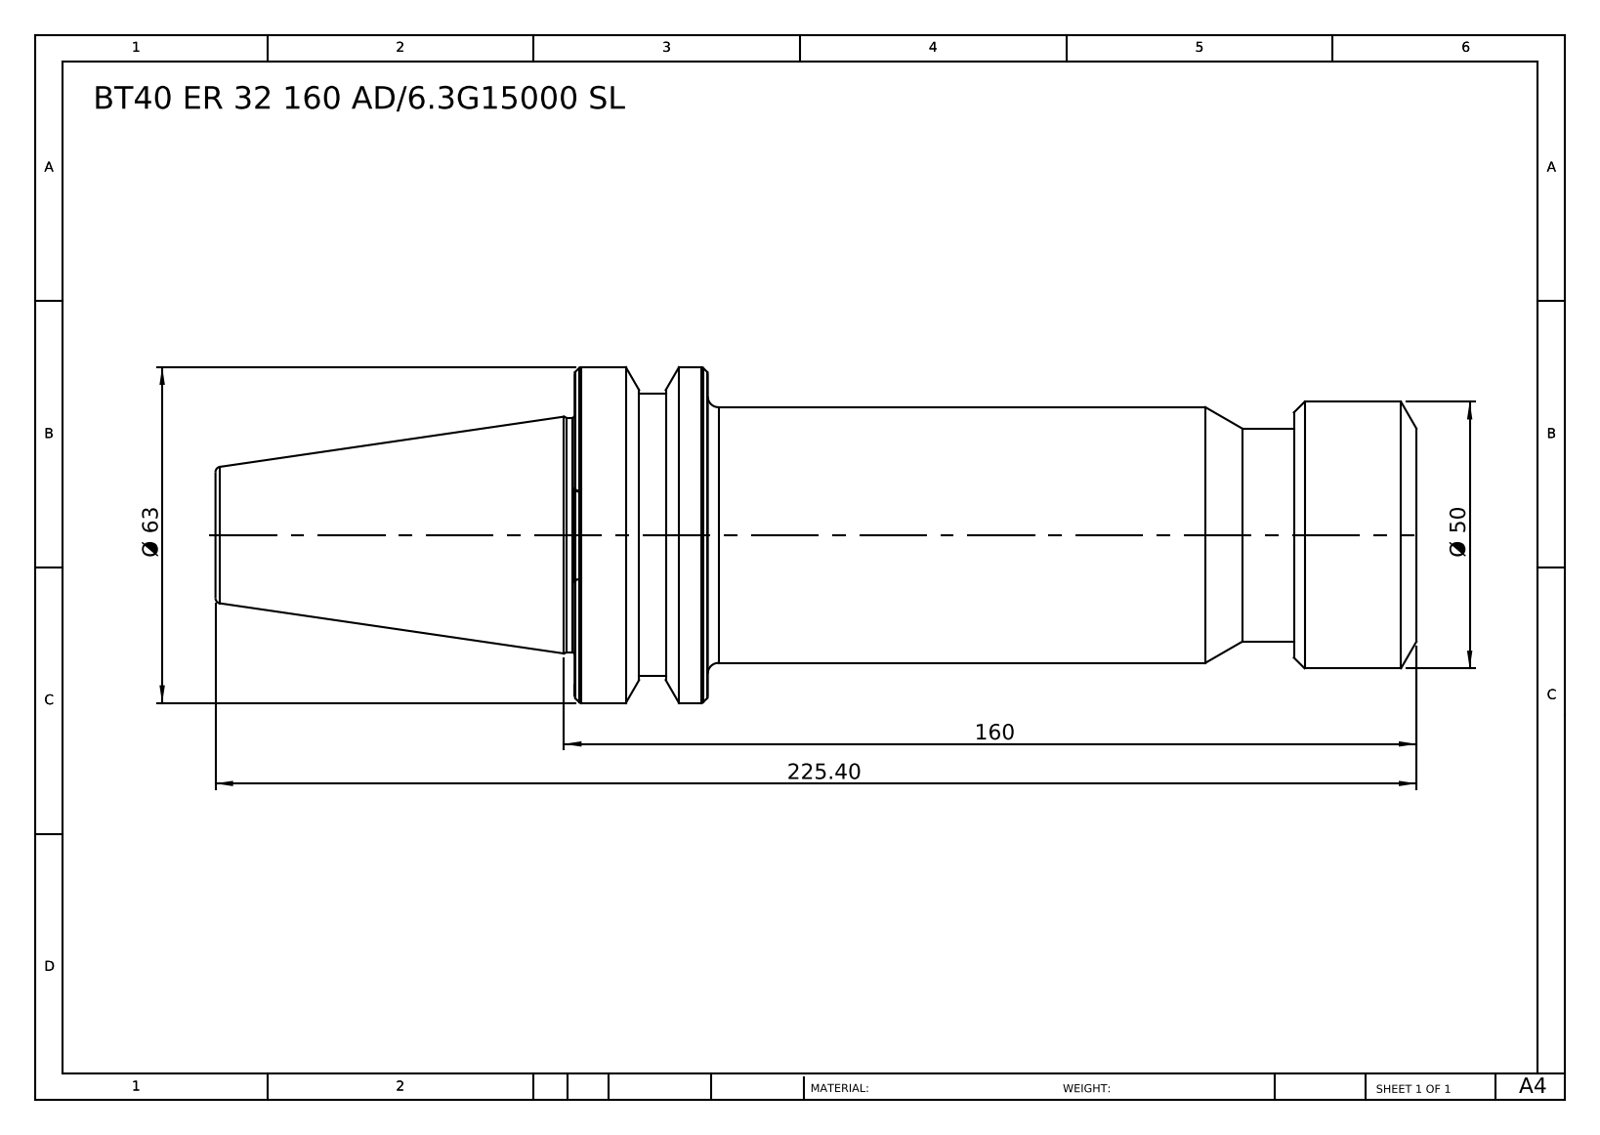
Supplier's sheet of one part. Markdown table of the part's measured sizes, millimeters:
| quantity | value |
| --- | --- |
| part name | BT40 ER 32 160 AD-6.3G15000 SL |
| STEP written by | SolidWorks 2014 (CONFIG_CONTROL_DESIGN) |
| units | millimeters |
| bodies | 1 solid, 62 faces (7 planar, 14 cylindrical, 41 other) |
| overall size | 225.4 × 63 × 63 |
| volume | 373 985 mm³ |
| surface area | 38 550 mm² |
| round bosses / shafts (diameter × count) | 63 × 1, 53 × 1, 50 × 1, 48 × 1, 44 × 1, 39.9 × 1 |
| main face-to-face distances | 158, 133, 25, 225.4, 92.4, 67.4, 23, 110, 135, 202.4 |
